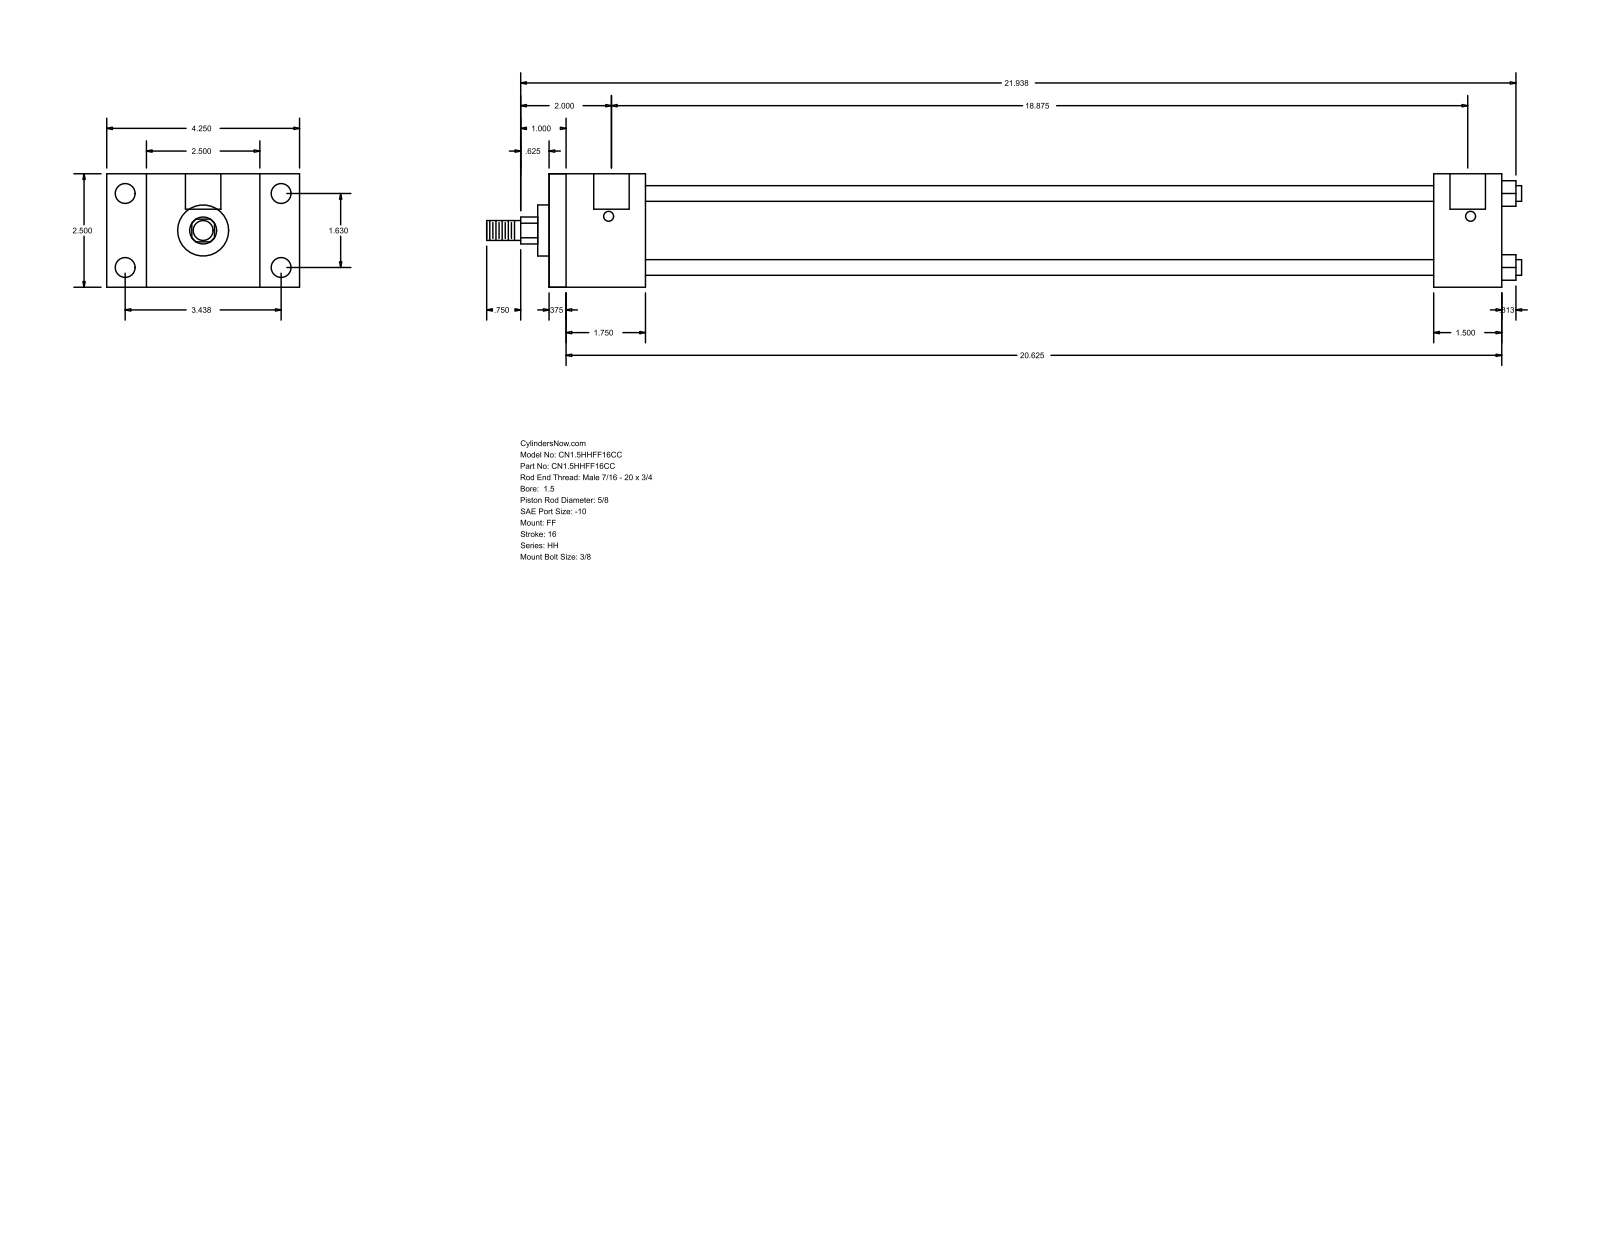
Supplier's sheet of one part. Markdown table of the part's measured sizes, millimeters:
| quantity | value |
| --- | --- |
| part name | HH_FF__0150_0.625 |
| STEP written by | GSSL Pune (CONFIG_CONTROL_DESIGN) |
| units | millimeters |
| bodies | 0 solids, 92 faces (64 planar, 28 cylindrical, 0 other) |
| overall size | 579.44 × 107.95 × 63.5 |
| round holes (diameter × count) | 5.56 × 4, 11.13 × 4, 19.84 × 2 |
| round bosses / shafts (diameter × count) | 8.76 × 4, 44.45 × 1, 28.57 × 1, 15.88 × 1, 11.11 × 1 |
| partial cylindrical surfaces (radius × count) | 7.54 × 1 |
| main face-to-face distances | 63.5, 533.39, 9.52, 523.87, 44.45, 53.97, 479.42, 495.3, 485.78, 441.33 |
| hole center spacings | 41.4, 87.32, 96.64, 482.6, 1.58, 1.59, 479.43, 481.01 |
